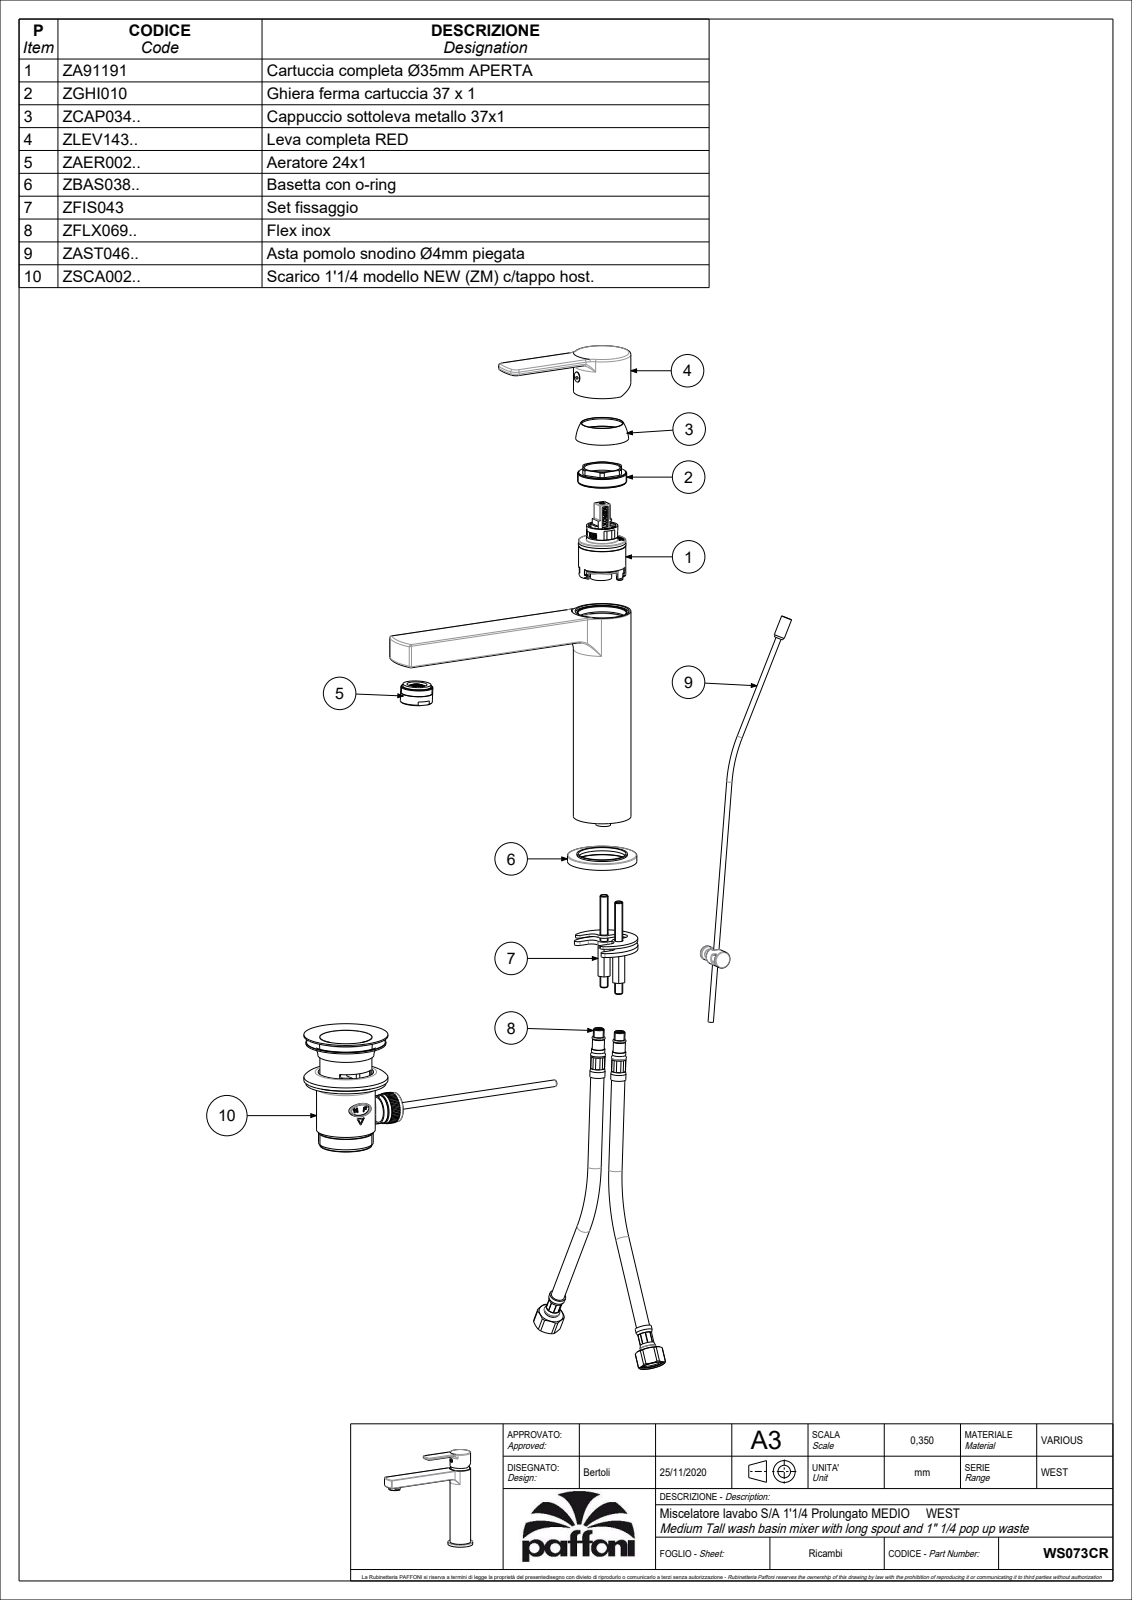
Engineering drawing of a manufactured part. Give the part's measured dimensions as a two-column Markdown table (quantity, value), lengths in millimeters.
| quantity | value |
| --- | --- |
| part name | WS073CR |
| STEP written by | CREO PARAMETRIC BY PTC INC, 2020044 (CONFIG_CONTROL_DESIGN) |
| units | millimeters |
| bodies | 5 solids, 3445 faces (2439 planar, 575 cylindrical, 431 other) |
| overall size | 218.97 × 200.55 × 52 |
| volume | 174 783 mm³ |
| surface area | 127 421 mm² |
| round holes (diameter × count) | 6 × 4, 8.2 × 4, 4 × 3, 5 × 3, 5.5 × 2, 6.5 × 2, 7 × 2, 8 × 2, 9 × 2, 3 × 1, 3.4 × 1, 3.5 × 1 |
| round bosses / shafts (diameter × count) | 8 × 7, 4 × 3, 11 × 2, 8.9 × 2, 6.5 × 2, 6 × 2, 4.8 × 2, 52 × 1 |
| partial cylindrical surfaces (radius × count) | 0.5 × 89, 1.5 × 16, 1 × 14, 1.7 × 6, 2 × 5, 0.8 × 4, 5.8 × 4, 12.75 × 3 |
| main face-to-face distances | 3, 14, 17, 27, 30, 11, 53.05, 36.05, 39.05, 50.05 |
| hole center spacings | 14, 13.6, 2.83, 8.6, 9.26, 11.77, 13.45, 15.13 |
